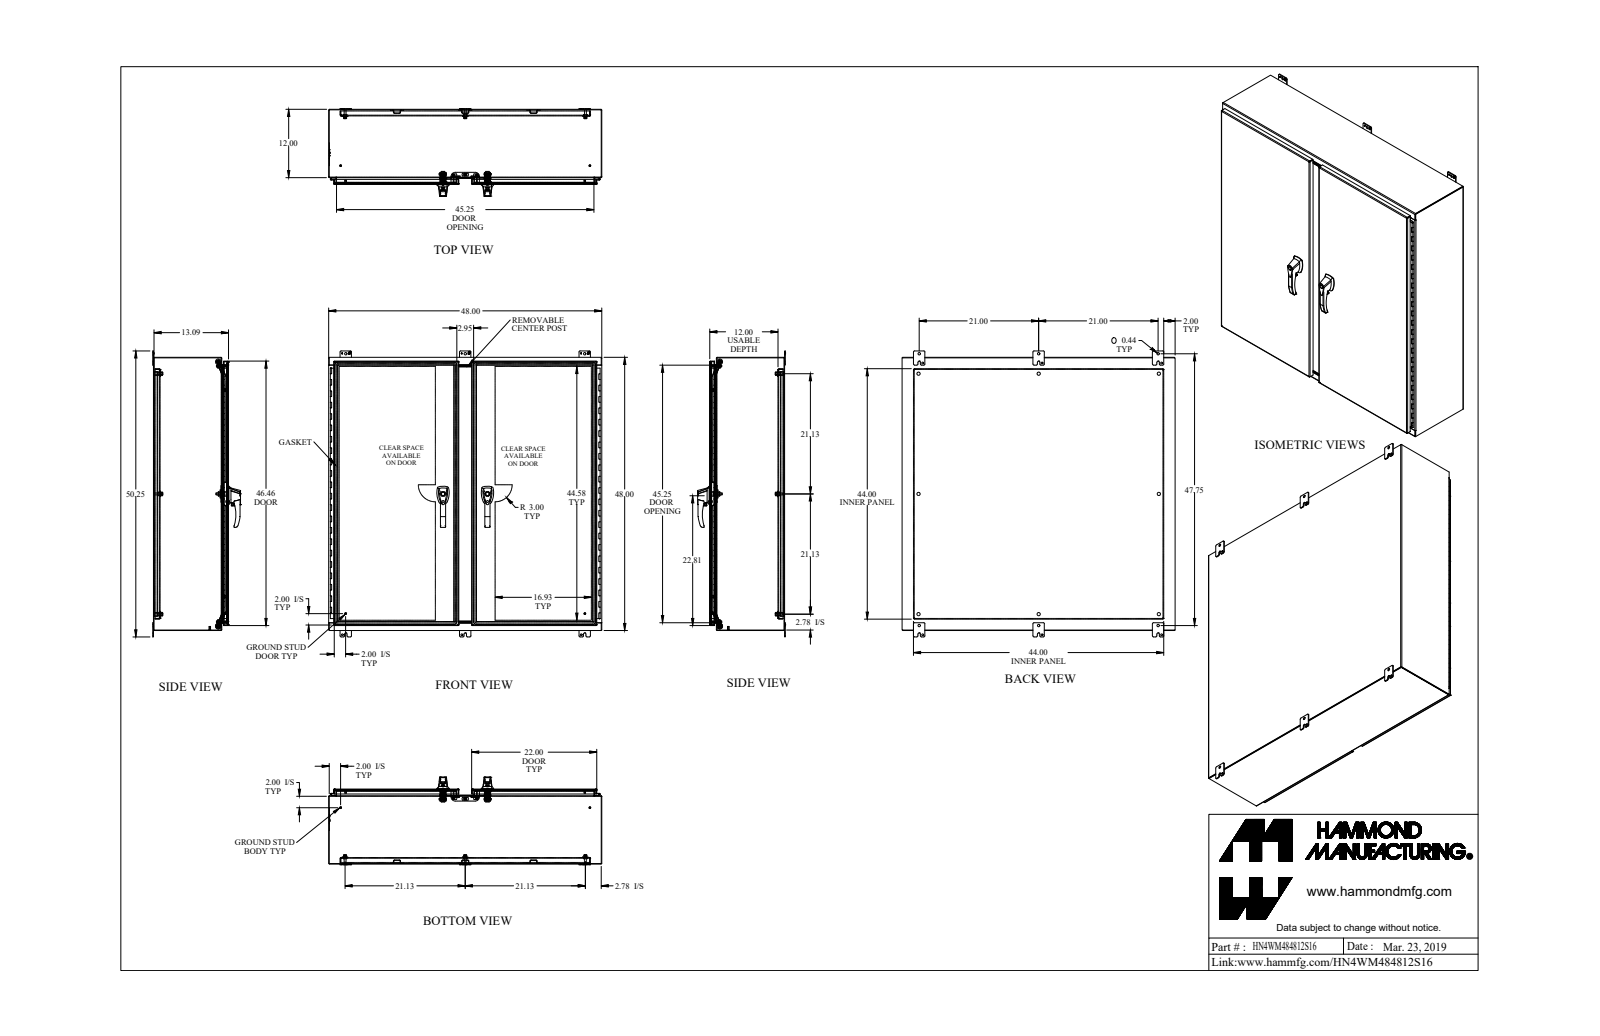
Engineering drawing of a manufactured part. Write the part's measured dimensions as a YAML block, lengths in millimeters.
part_name: "HN4WM484812S16"
step_written_by: "SolidWorks 2018 (AUTOMOTIVE_DESIGN)"
units: millimeters
bodies: {solids: 120, faces: 3482, planar: 1616, cylindrical: 1457, other: 409}
overall_size: [1276.4, 1219.2, 391.8]
volume: 18070000
surface_area: 14200000
round_holes:
  - {diameter: 7.7, count: 16}
  - {diameter: 7.8, count: 8}
  - {diameter: 14.3, count: 8}
  - {diameter: 6.4, count: 6}
  - {diameter: 8, count: 6}
  - {diameter: 11.3, count: 6}
  - {diameter: 7.1, count: 4}
  - {diameter: 8, count: 4}
  - {diameter: 9.9, count: 4}
  - {diameter: 5.1, count: 3}
  - {diameter: 11.1, count: 3}
  - {diameter: 2.8, count: 2}
round_bosses_or_shafts:
  - {diameter: 25.4, count: 10}
  - {diameter: 16.5, count: 8}
  - {diameter: 9.5, count: 8}
  - {diameter: 8.4, count: 8}
  - {diameter: 19.1, count: 4}
  - {diameter: 15.9, count: 4}
  - {diameter: 11.2, count: 4}
  - {diameter: 9.4, count: 4}
partial_cylinders:
  - {radius: 3.2, count: 35}
  - {radius: 4.8, count: 33}
  - {radius: 0.5, count: 32}
  - {radius: 6.4, count: 26}
  - {radius: 1.5, count: 24}
  - {radius: 1.2, count: 17}
  - {radius: 3.6, count: 17}
  - {radius: 12.7, count: 17}
face_to_face_distances: [2.4, 1216.8, 2.4, 332.5, 330.1, 334.9, 332.5, 23.8, 29.4, 3.2]
hole_center_spacings: [152.4, 1181.3, 304.8, 1210.4, 536.6, 457.2, 1257.5, 1199.8]
